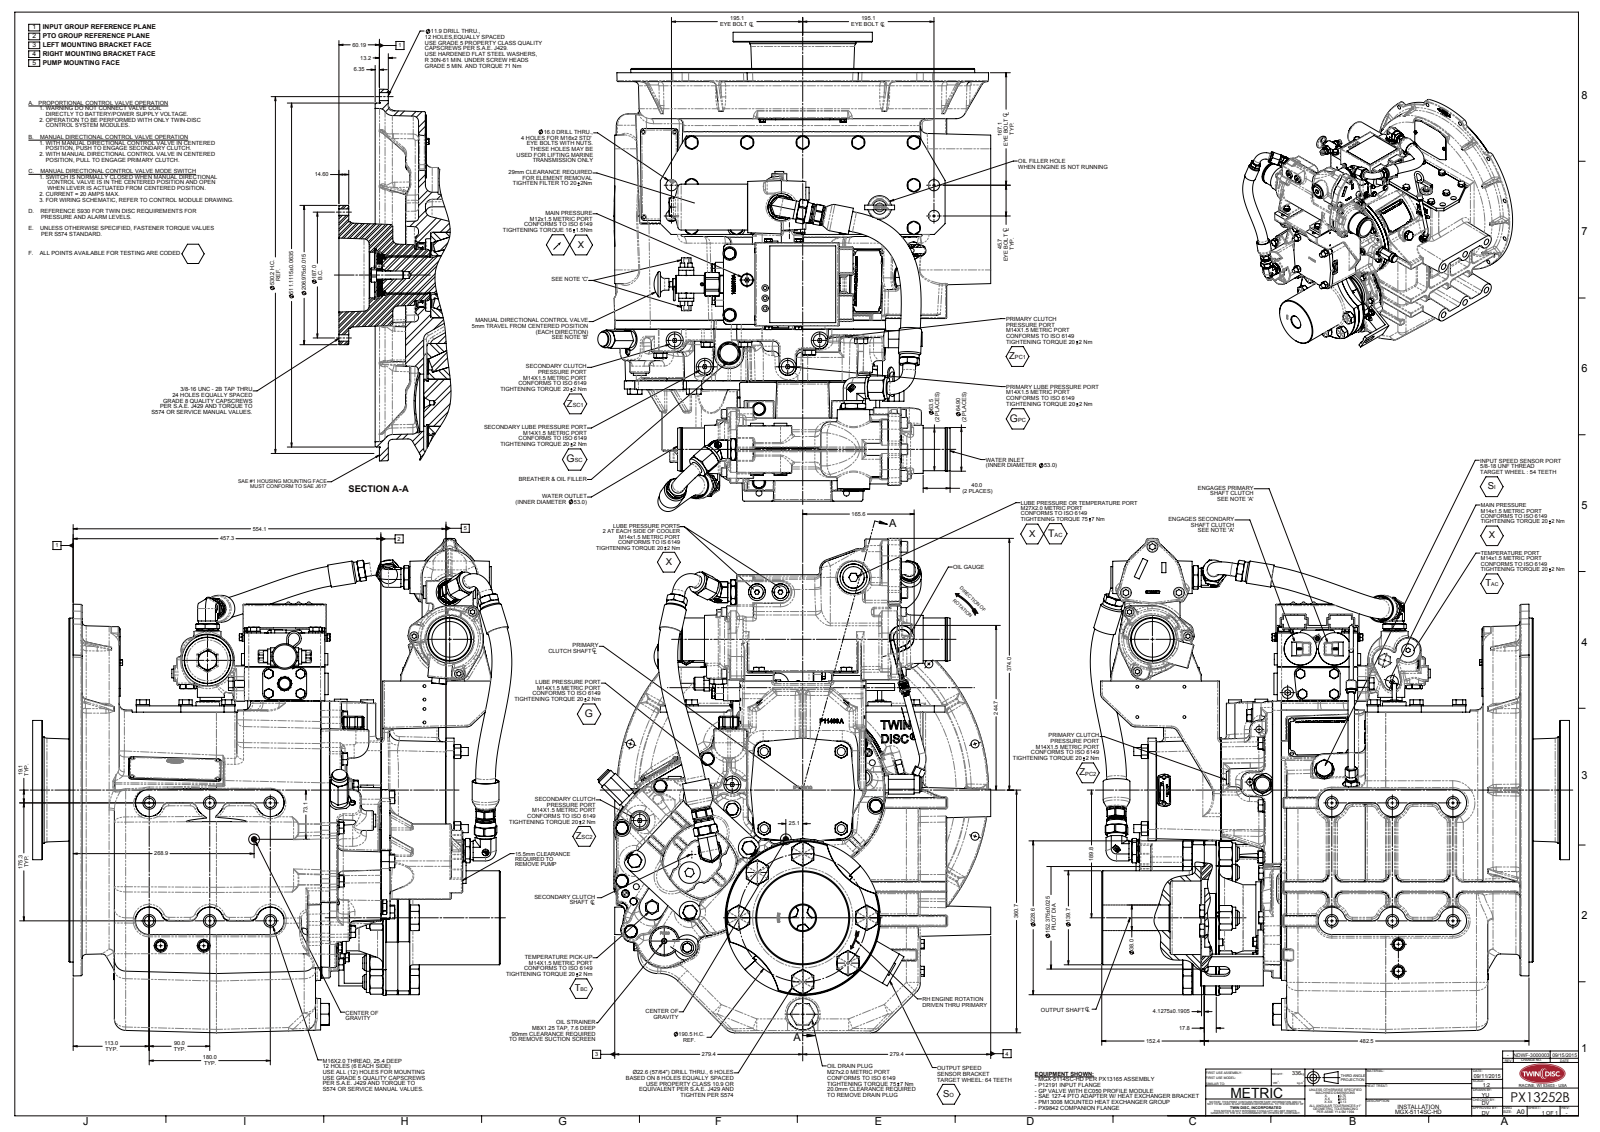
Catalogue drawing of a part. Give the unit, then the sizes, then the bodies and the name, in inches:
Units: inches
Overall size (bounding box): 28.924 × 28.039 × 22.993
Round holes (diameter × count): ⌀0.375 ×24, ⌀0.469 ×12, ⌀0.165 ×7, ⌀0.346 ×7, ⌀0.741 ×6, ⌀0.984 ×5, ⌀0.656 ×4, ⌀0.366 ×3, ⌀0.394 ×3, ⌀1 ×3, ⌀0.189 ×2, ⌀0.397 ×2
Round bosses / shafts (diameter × count): ⌀0.787 ×23, ⌀0.748 ×11, ⌀0.75 ×8, ⌀0.512 ×8, ⌀1.246 ×5, ⌀0.781 ×5, ⌀0.472 ×5, ⌀0.1 ×5
Partial cylindrical surfaces — rounded edges, fillets, slot ends (radius × count): R0.793 ×327, R0.05 ×145, R0.06 ×90, R0.039 ×68, R0.4 ×67, R0.079 ×66, R0.32 ×46, R0.157 ×45
Main face-to-face distances: 0.017, 0.517, 12.723, 12.706, 0.533, 12.19, 0.365, 0.5, 12.206, 12.323
Hole centre spacings: 18.078, 5.403, 10.437, 14.761, 20.163, 11.932, 14.026, 8.256
Bodies: 0 solids, 7721 faces (2508 planar, 2565 cylindrical, 2648 other)
Part name (STEP PRODUCT): PX13252B
STEP written by: SolidWorks 2010 (AUTOMOTIVE_DESIGN)
